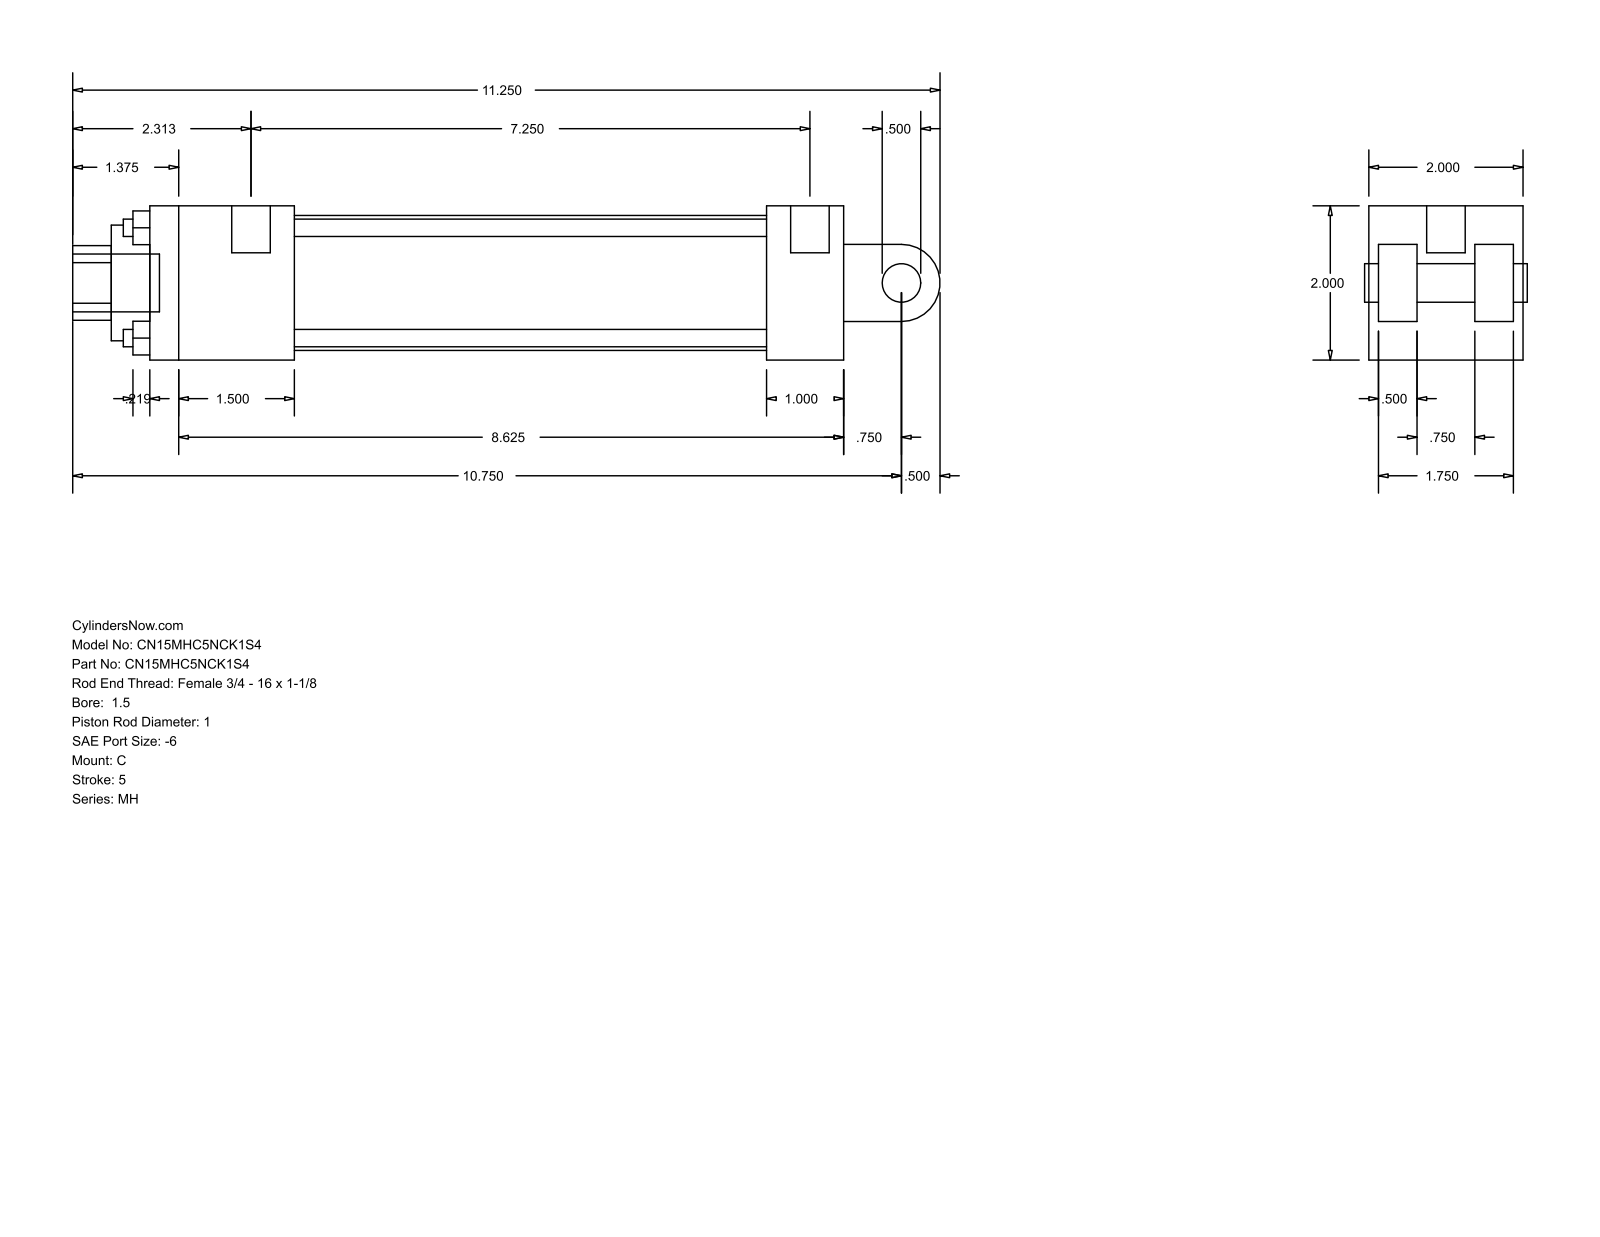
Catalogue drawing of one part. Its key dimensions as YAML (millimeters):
part_name: "MH_C__0150_1"
step_written_by: "GSSL Pune (CONFIG_CONTROL_DESIGN)"
units: millimeters
bodies: {solids: 0, faces: 99, planar: 70, cylindrical: 29, other: 0}
overall_size: [285.75, 50.8, 50.8]
round_holes:
  - {diameter: 5.71, count: 4}
  - {diameter: 5.56, count: 2}
  - {diameter: 12.7, count: 1}
  - {diameter: 25.4, count: 1}
  - {diameter: 38.1, count: 1}
  - {diameter: 44.45, count: 1}
round_bosses_or_shafts:
  - {diameter: 12.7, count: 2}
  - {diameter: 5.56, count: 2}
  - {diameter: 19.05, count: 1}
partial_cylinders:
  - {radius: 12.29, count: 1}
  - {radius: 12.7, count: 1}
face_to_face_distances: [50.8, 12.7, 47.63, 3.17, 15.87, 25.4, 34.93, 31.76, 228.6, 38.1]
hole_center_spacings: [25.68, 36.32, 51.36]
